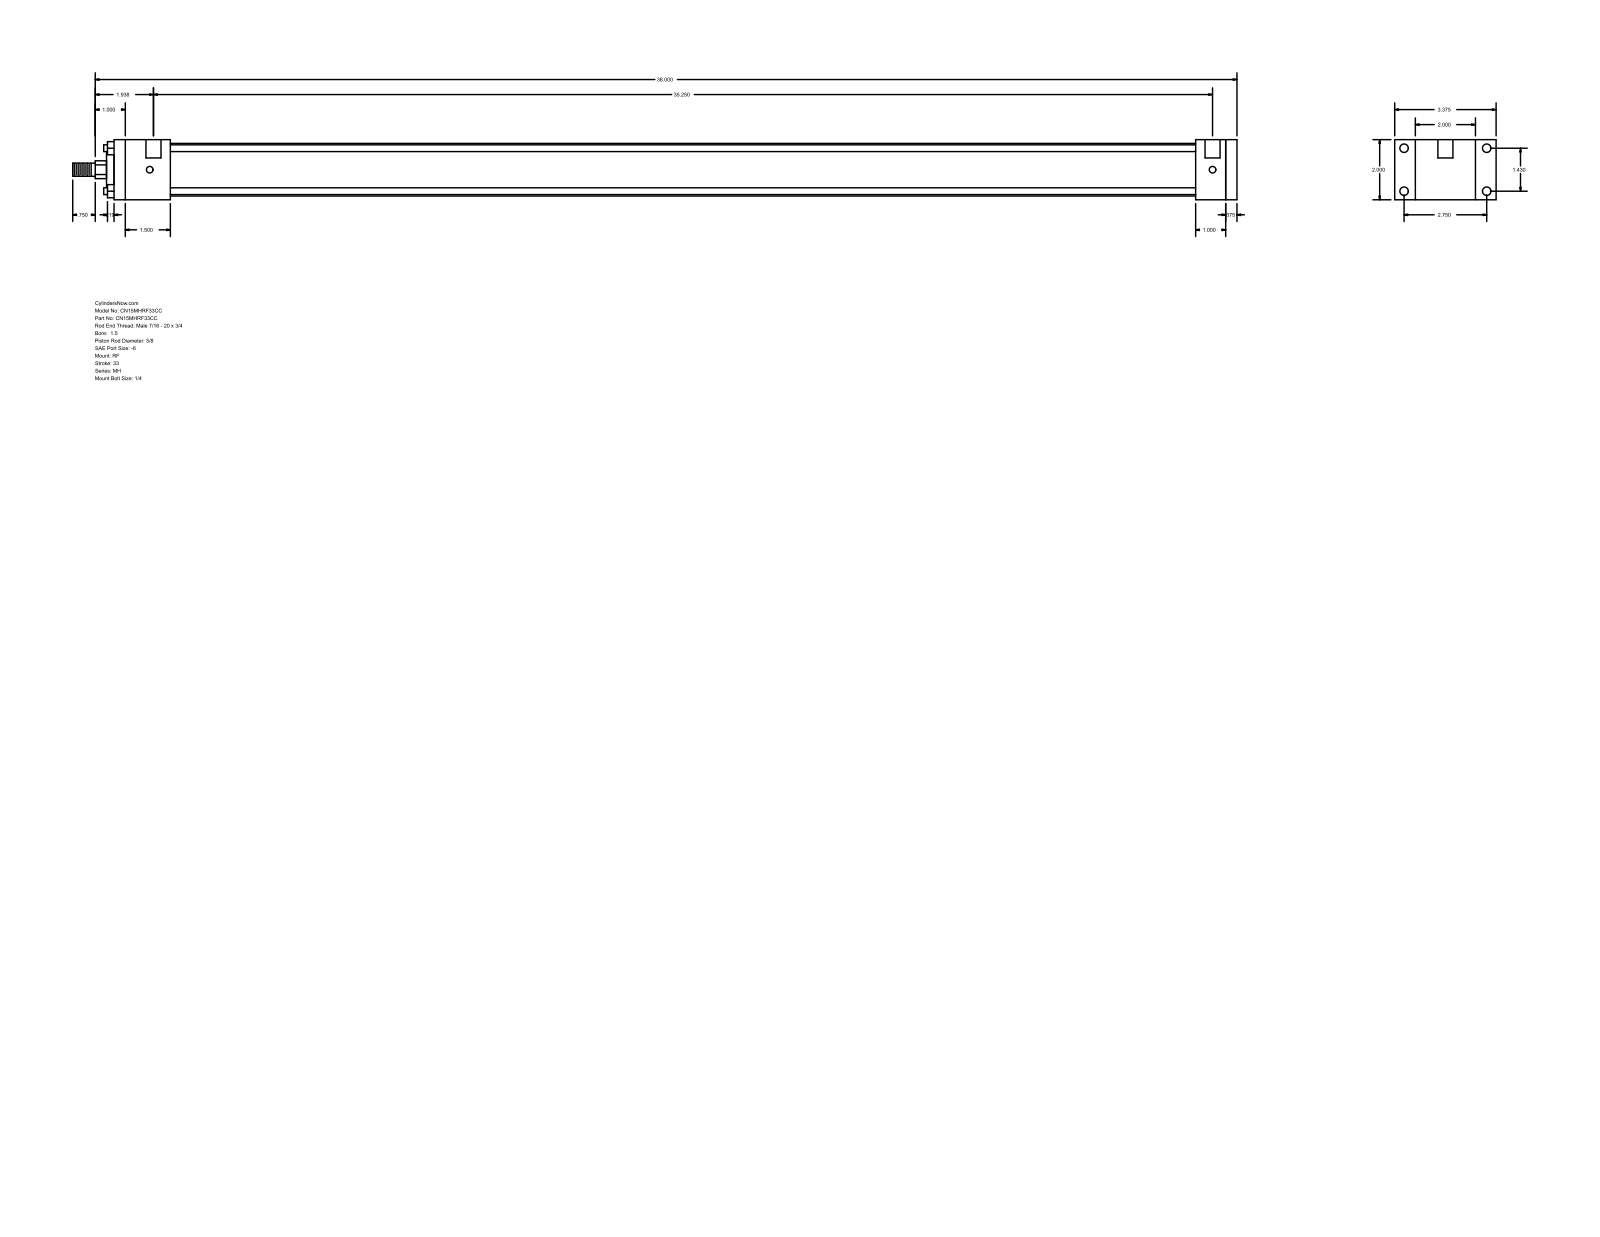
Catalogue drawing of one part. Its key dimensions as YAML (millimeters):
part_name: "MH_RF__0150_0.625"
step_written_by: "GSSL Pune (CONFIG_CONTROL_DESIGN)"
units: millimeters
bodies: {solids: 0, faces: 92, planar: 64, cylindrical: 28, other: 0}
overall_size: [984.25, 85.72, 50.8]
round_holes:
  - {diameter: 5.56, count: 4}
  - {diameter: 7.14, count: 4}
  - {diameter: 12.7, count: 2}
round_bosses_or_shafts:
  - {diameter: 5.71, count: 4}
  - {diameter: 44.45, count: 1}
  - {diameter: 28.57, count: 1}
  - {diameter: 15.88, count: 1}
  - {diameter: 11.11, count: 1}
partial_cylinders:
  - {radius: 7.54, count: 1}
face_to_face_distances: [50.8, 9.53, 949.32, 939.79, 34.93, 25.4, 17.46, 68.26, 914.39, 47.62]
hole_center_spacings: [36.32, 69.84, 78.72, 898.52, 3.17, 895.35]
